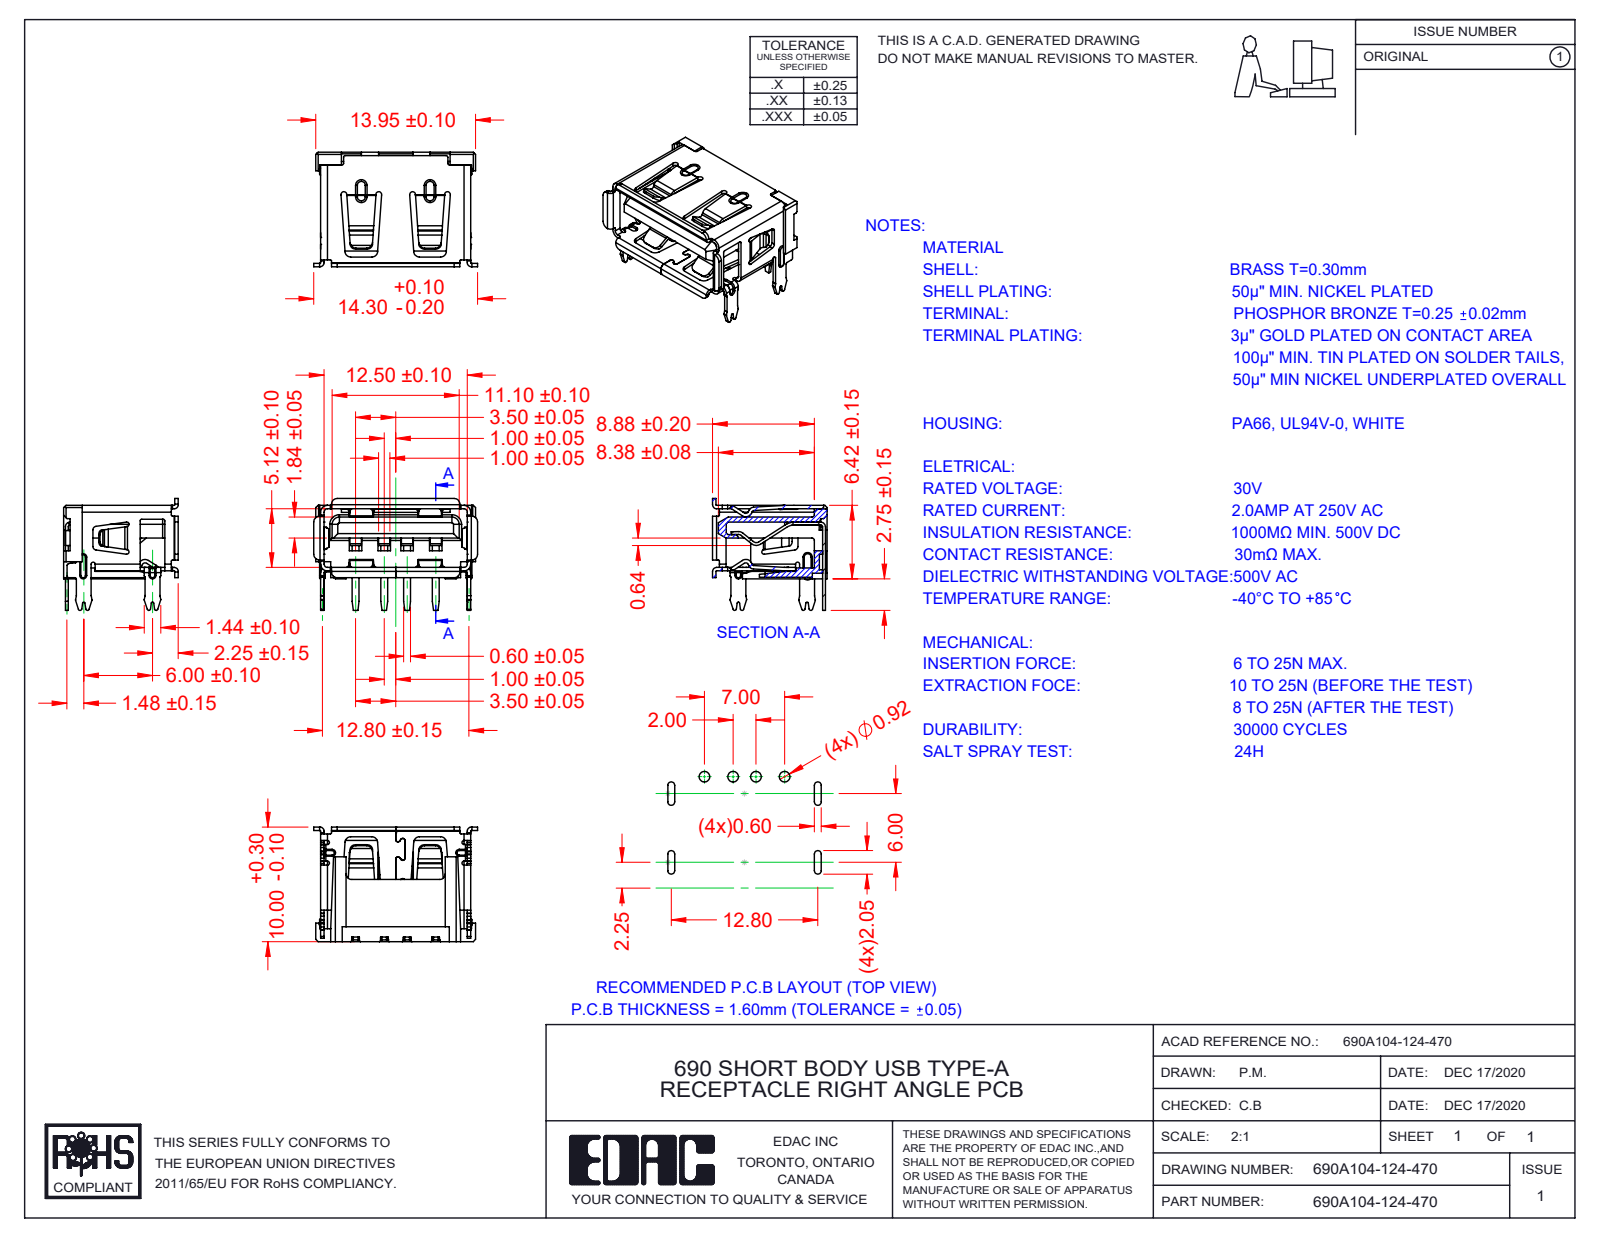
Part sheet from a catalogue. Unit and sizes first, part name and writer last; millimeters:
Units: millimetres
Overall size (bounding box): 14.3 × 10 × 9.77
Partial cylindrical surfaces — rounded edges, fillets, slot ends (radius × count): R0.13 ×72, R0.1 ×51, R0.2 ×35, R0.15 ×31, R0.5 ×25, R0.25 ×22, R0.26 ×8, R0.3 ×8
Main face-to-face distances: 5.42, 2.5, 1.03, 0.73, 0.45, 12.8, 2.57, 1.39, 1.84, 2.87
Volume: 310 mm³ · Surface area: 1 489 mm²
Bodies: 6 solids, 1233 faces (714 planar, 451 cylindrical, 68 other)
Part name (STEP PRODUCT): Shell 690A104-124-470; Contact 690A104-124-470; Insulator 690A104-124-470; 690A104-124-470
STEP written by: SolidWorks 2020 (AUTOMOTIVE_DESIGN)
